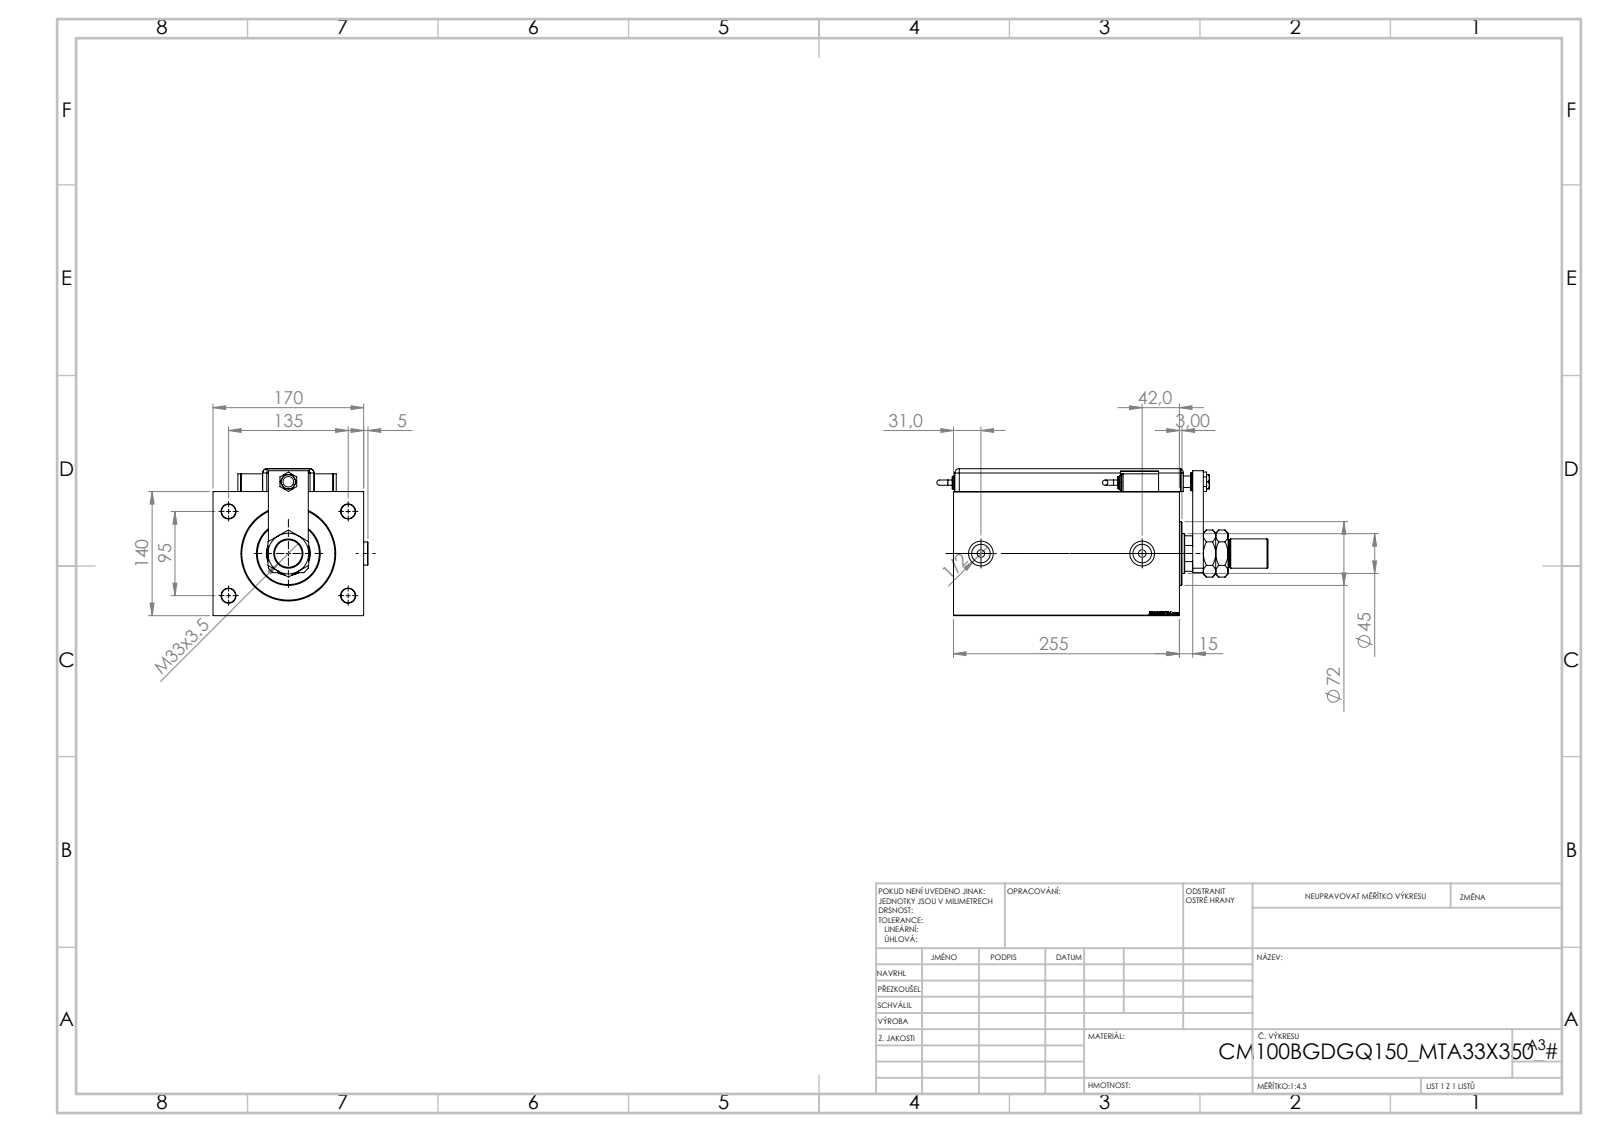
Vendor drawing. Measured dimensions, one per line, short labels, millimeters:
name: MAGNETIC SWITCH Q; V450CM_B_Body; ZARAZKA_Q; NUT_D19 (+7 more)
written by: SolidWorks 2019 (CONFIG_CONTROL_DESIGN)
unit: mm
bodies: 16 solids, 1371 faces (657 planar, 131 cylindrical, 583 other)
size: 373.76 × 174.9 × 165.8
volume: 5 395 000 mm³; area: 498 600 mm²
holes: 4× ⌀16, 2× ⌀4, 2× ⌀8, 2× ⌀8.5, 2× ⌀20.96, 2× ⌀28, 1× ⌀12, 1× ⌀13, 1× ⌀14, 1× ⌀31.5, 1× ⌀33, 1× ⌀45
bosses: 3× ⌀20, 2× ⌀26, 2× ⌀16, 2× ⌀14, 2× ⌀6, 1× ⌀72, 1× ⌀31
rounds: 9× R5, 1× R10, 1× R22
face distances: 140, 170, 3, 255, 26, 229, 15, 25.8, 165.8, 162.8
hole spacings: 82.54, 75.36, 95, 135, 145.15, 165.08, 20, 81
